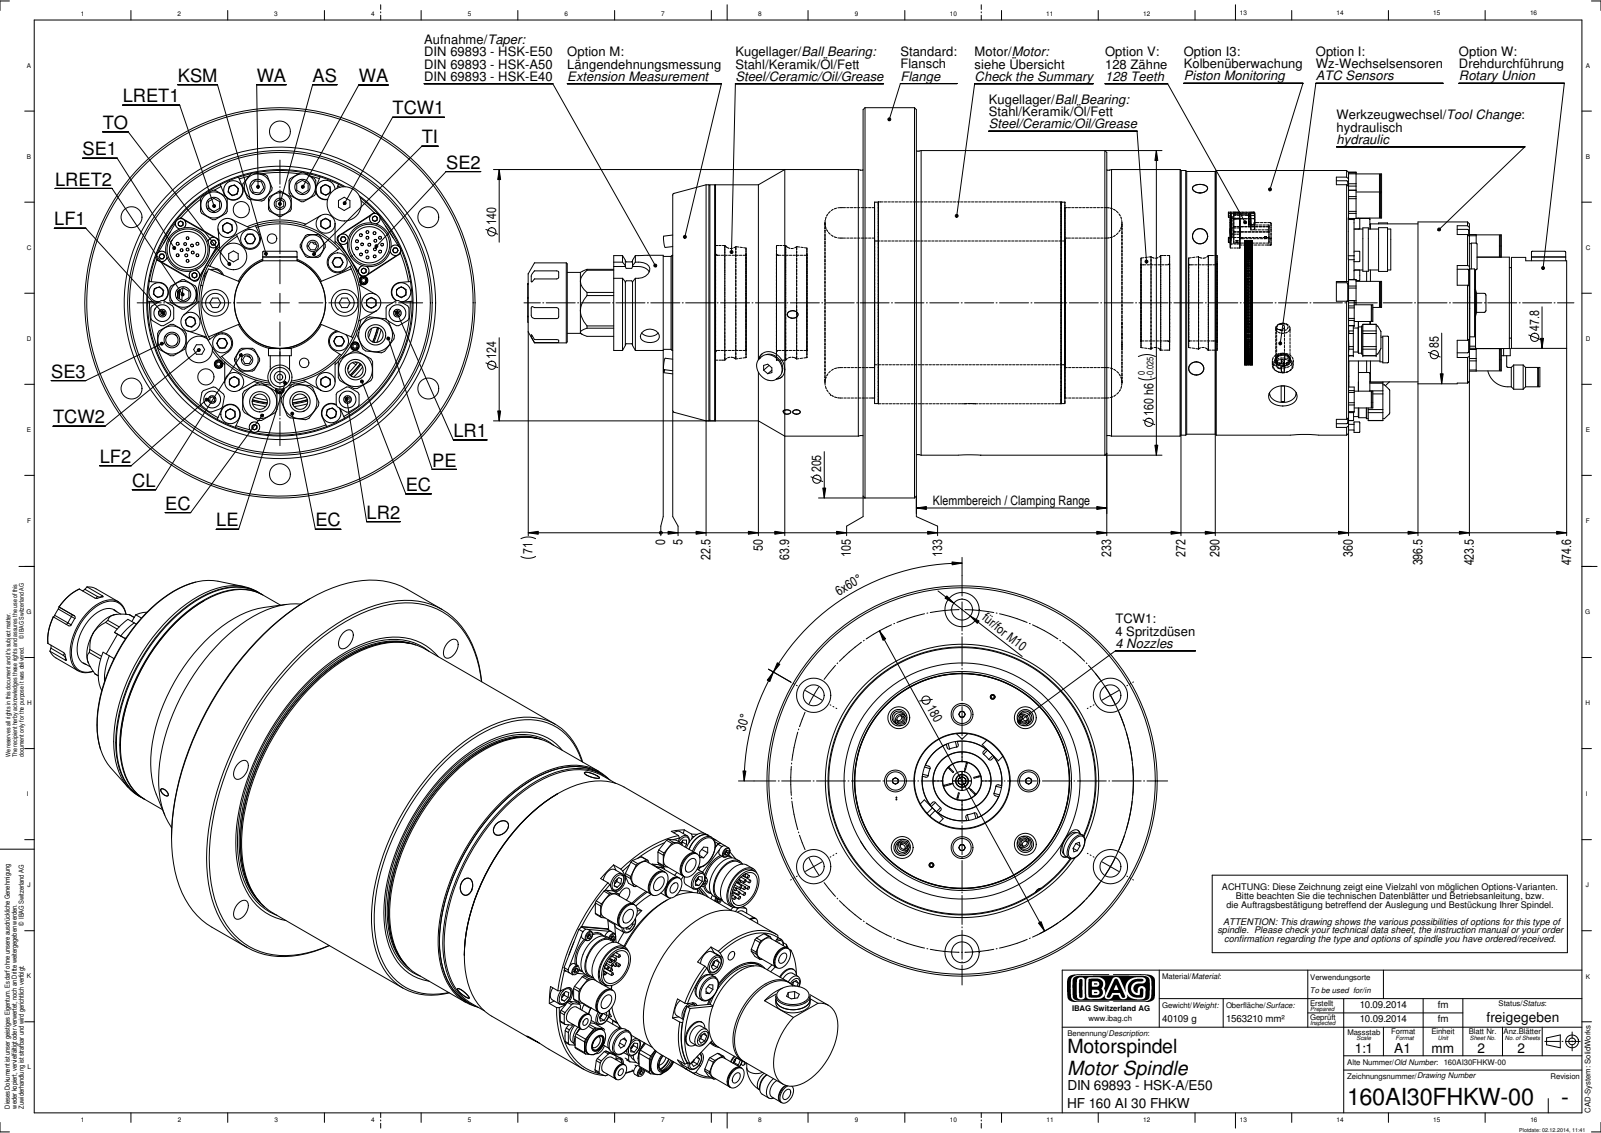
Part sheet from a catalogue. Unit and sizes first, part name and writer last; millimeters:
Units: millimetres
Overall size (bounding box): 545.76 × 205 × 205
Round holes (diameter × count): ⌀8 ×8, ⌀4.5 ×7, ⌀11 ×6, ⌀18 ×6, ⌀4 ×4, ⌀6 ×4, ⌀10.7 ×4, ⌀11.5 ×4, ⌀15 ×4, ⌀16.2 ×4, ⌀8.5 ×3, ⌀5 ×2
Round bosses / shafts (diameter × count): ⌀1.5 ×29, ⌀10 ×20, ⌀5.5 ×9, ⌀14 ×5, ⌀17.8 ×4, ⌀16.79 ×4, ⌀15.59 ×4, ⌀13.7 ×4
Partial cylindrical surfaces — rounded edges, fillets, slot ends (radius × count): R1 ×12, R6.6 ×7, R5.2 ×6, R5.5 ×6, R6 ×4, R7.75 ×4, R9.9 ×4, R6.5 ×1
Main face-to-face distances: 28, 100, 128, 167, 139, 267, 355, 255, 227, 88
Hole centre spacings: 90, 53, 62, 155.88, 52.93, 67.73, 88.78, 113.65
Bodies: 0 solids, 1599 faces (611 planar, 644 cylindrical, 344 other)
Part name (STEP PRODUCT): 160AI30FHKW-00
STEP written by: SolidWorks 2014 (CONFIG_CONTROL_DESIGN)
